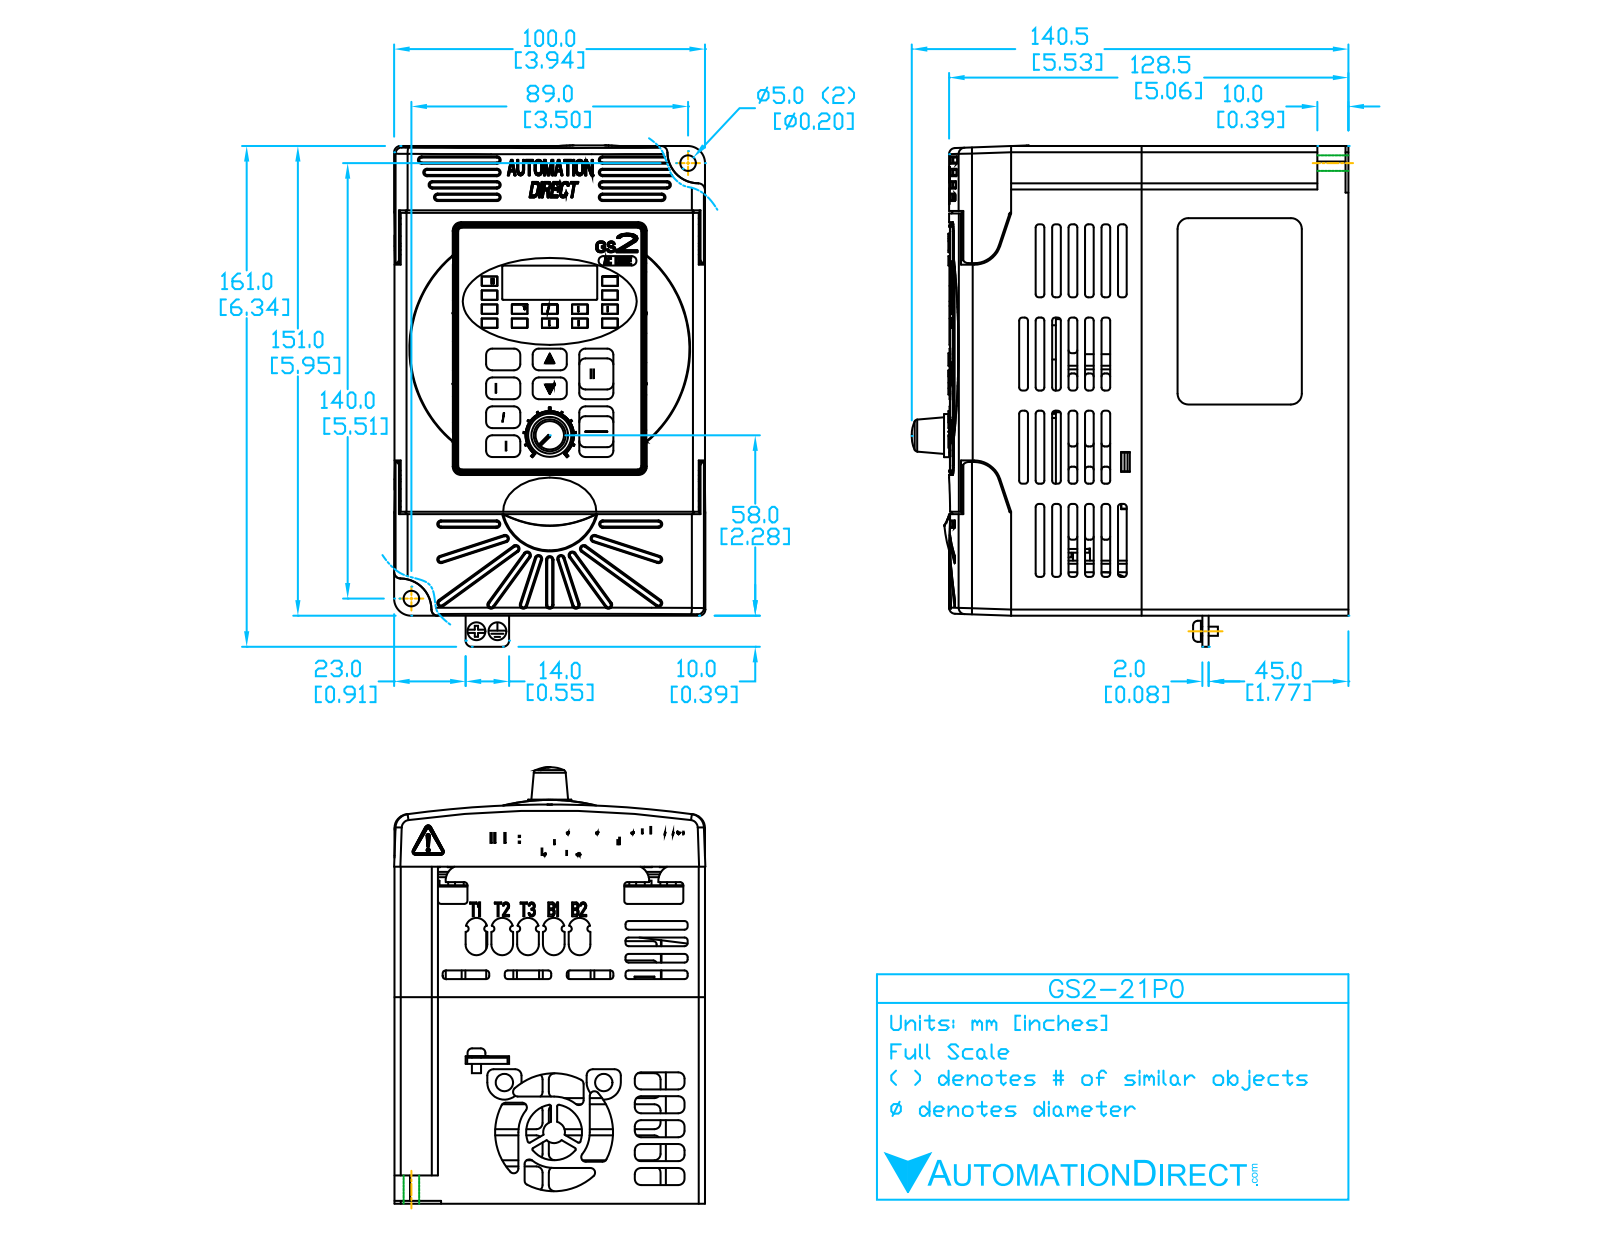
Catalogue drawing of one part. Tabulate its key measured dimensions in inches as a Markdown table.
| quantity | value |
| --- | --- |
| part name | GS2-21P0 |
| STEP written by | SolidWorks 2013 (AUTOMOTIVE_DESIGN) |
| units | inches |
| bodies | 1 solid, 747 faces (324 planar, 220 cylindrical, 203 other) |
| overall size | 6.345 × 5.495 × 3.94 |
| volume | 112.9 in³ |
| surface area | 196.7 in² |
| round holes (diameter × count) | 0.2 × 2, 0.7 × 1, 1.46 × 1 |
| round bosses / shafts (diameter × count) | 0.545 × 1, 0.22 × 1, 0.15 × 1 |
| partial cylindrical surfaces (radius × count) | 0.04 × 40, 0.06 × 16, 0.03 × 14, 0.125 × 10, 0.03 × 8, 0.045 × 6, 0.2 × 6, 0.1 × 4 |
| main face-to-face distances | 3.94, 5.95, 4.256, 4.266, 0.015, 5.935, 0.03, 0.761, 3.179, 0.03 |
| hole center spacings | 6.528 |
